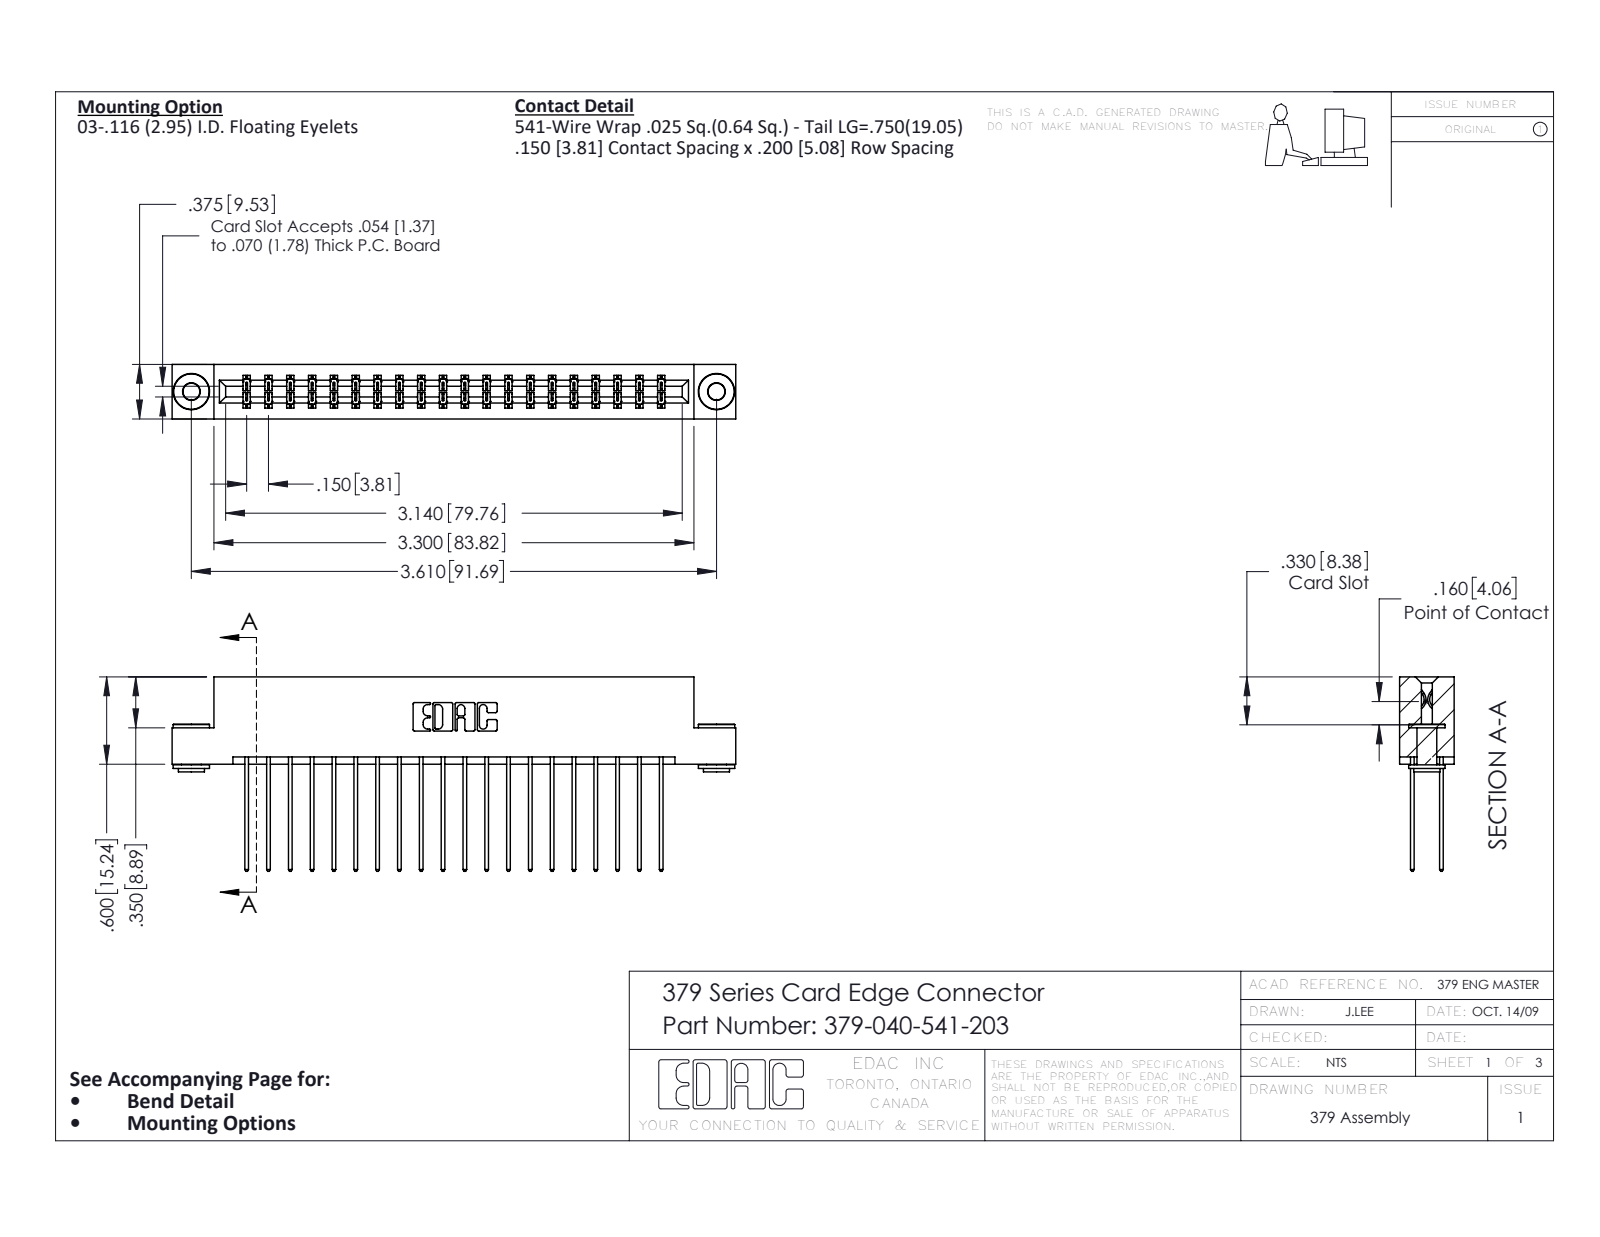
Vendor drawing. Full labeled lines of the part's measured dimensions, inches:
Part name (STEP PRODUCT): 379-040-541-203; 345-250-002_345-250-002-102; 345-292-001_345-293-141; 379 Part_Flush - .156 Dia - TH
STEP written by: SolidWorks 2016 (CONFIG_CONTROL_DESIGN)
Units: inches
Bodies: 43 solids, 2232 faces (1520 planar, 704 cylindrical, 8 other)
Overall size (bounding box): 3.875 × 1.337 × 0.375
Volume: 0.638 in³ · Surface area: 20.03 in²
Round holes (diameter × count): ⌀0.116 ×2, ⌀0.156 ×2
Round bosses / shafts (diameter × count): ⌀0.25 ×2, ⌀0.18 ×2, ⌀0.136 ×2
Partial cylindrical surfaces — rounded edges, fillets, slot ends (radius × count): R0.006 ×60, R0.01 ×40, R0.01 ×22, R0.007 ×6, R0.031 ×6, R0.026 ×3, R0.014 ×2, R0.022 ×2
Main face-to-face distances: 0.3, 0.075, 0.2, 0.1, 0.375, 0.275, 0.025, 0.076, 0.15, 0.225
Hole centre spacings: 3.61
